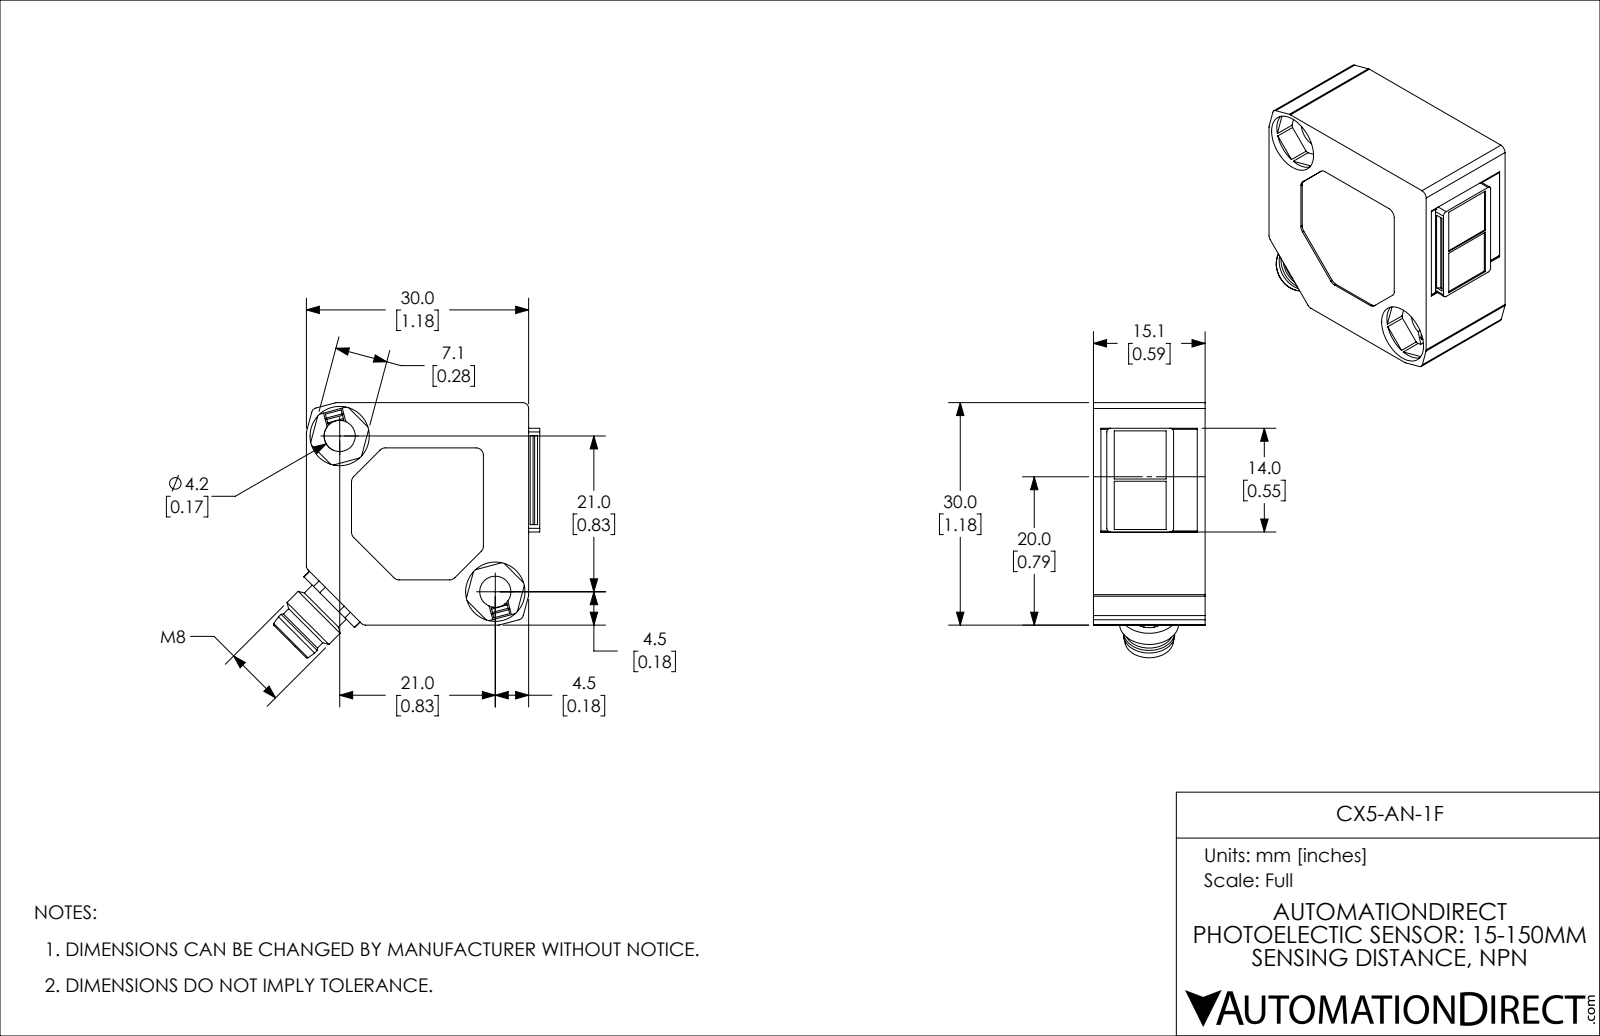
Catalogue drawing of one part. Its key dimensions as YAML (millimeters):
part_name: "LHS_3031_301"
step_written_by: "SolidWorks 2021 (AUTOMOTIVE_DESIGN)"
units: millimeters
bodies: {solids: 1, faces: 209, planar: 123, cylindrical: 68, other: 18}
overall_size: [39.45, 34.45, 15]
volume: 12797
surface_area: 4678
round_holes:
  - {diameter: 2.2, count: 2}
  - {diameter: 4.2, count: 2}
  - {diameter: 8, count: 2}
  - {diameter: 1.85, count: 1}
  - {diameter: 5.8, count: 1}
  - {diameter: 7.6, count: 1}
round_bosses_or_shafts:
  - {diameter: 1, count: 3}
  - {diameter: 8, count: 1}
  - {diameter: 6.9, count: 1}
  - {diameter: 6.5, count: 1}
partial_cylinders:
  - {radius: 0.8, count: 9}
  - {radius: 1, count: 7}
  - {radius: 0.2, count: 4}
  - {radius: 0.15, count: 2}
  - {radius: 0.3, count: 2}
  - {radius: 0.46, count: 2}
  - {radius: 4.85, count: 1}
face_to_face_distances: [15, 30, 14.75, 11.2, 3.8, 3.55, 7.1, 0.92, 33.75, 5]
hole_center_spacings: [1.73, 4.4, 5, 5.47, 5.86, 5.96, 29.7]
